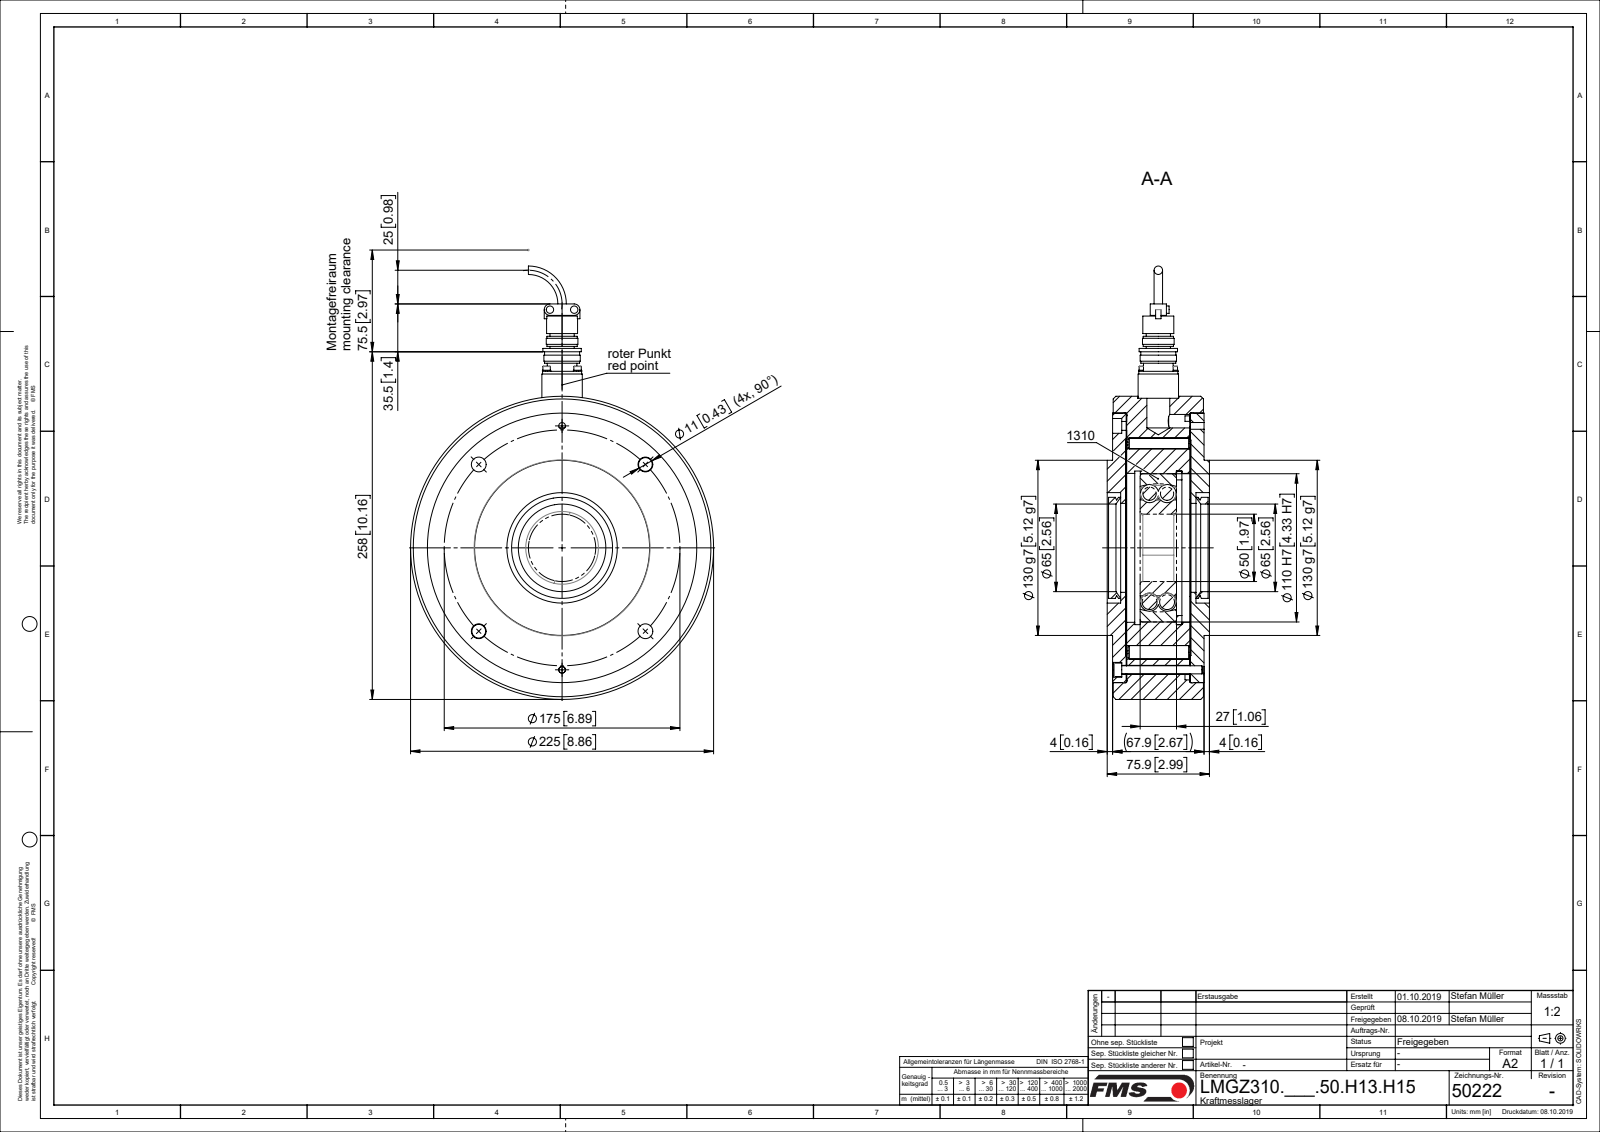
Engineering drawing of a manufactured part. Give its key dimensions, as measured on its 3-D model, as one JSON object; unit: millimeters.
{"part_name": "L50222; L49152; TEIL1; L49153 (+8 more)", "step_written_by": "Mechanical Desktop 2007 (CONFIG_CONTROL_DESIGN)", "units": "millimeters", "bodies": {"solids": 20, "faces": 403, "planar": 111, "cylindrical": 234, "other": 58}, "overall_size": [321.65, 225, 75.9], "volume_mm3": 2413000, "surface_area_mm2": 389245, "round_holes": [[11, 6], [2.6, 4], [3.2, 4], [3.4, 4], [9, 4], [5, 2], [6.6, 2], [23, 1], [50, 1], [64, 1], [66, 1], [82, 1]], "round_bosses_or_shafts": [[5.5, 6], [6.2, 4], [3, 4], [2.5, 4], [225, 1], [199, 1], [130, 1], [74, 1]], "partial_cylinders_radius": [[4.25, 2], [81, 1], [86, 1]], "face_to_face_distances": [9.7, 47.25, 10.45, 10.75, 47.45, 10.2, 57.45, 57.7, 47, 10], "hole_center_spacings": [16.26, 23, 87.5, 32.53, 68.17, 68.18, 90.5, 123.74]}
